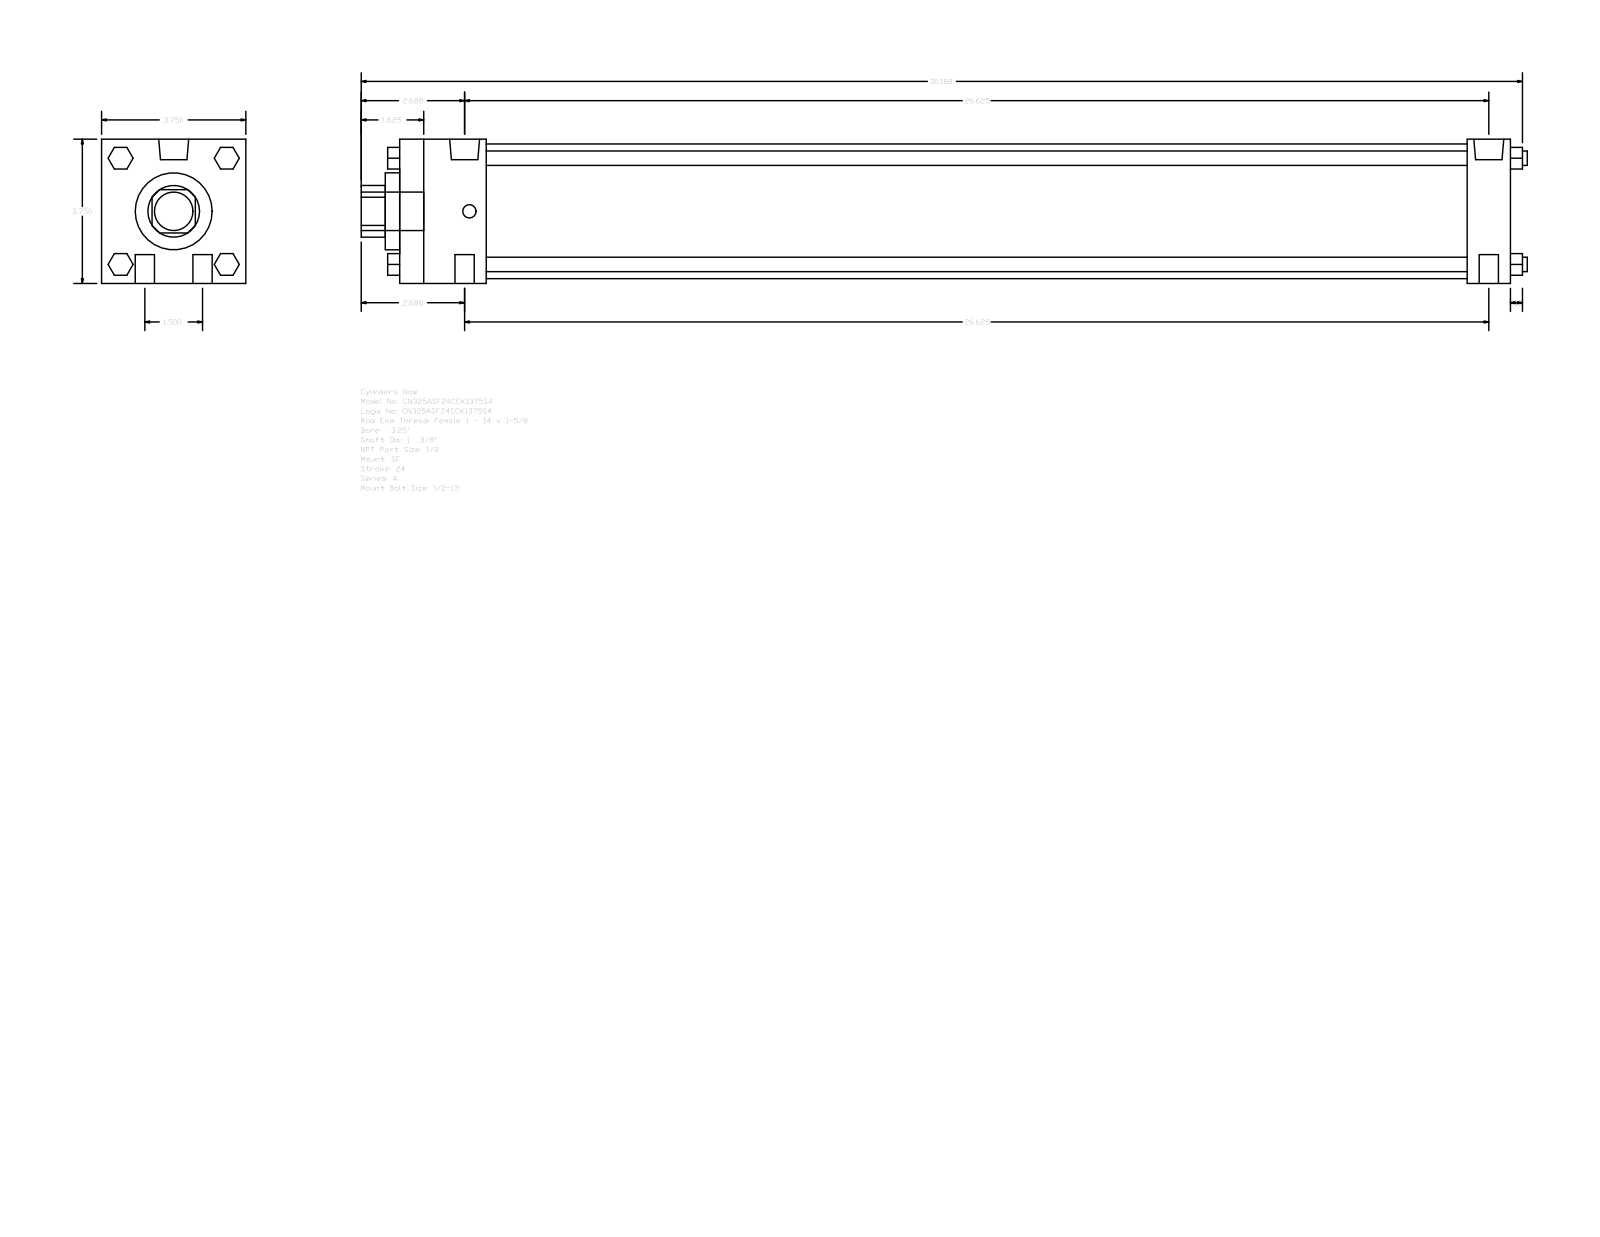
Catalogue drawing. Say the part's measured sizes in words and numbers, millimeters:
The part is named "A_SF__0325_1.375". Its 3-D file was written by "GSSL Pune (CONFIG_CONTROL_DESIGN)". It is 0 solids with 124 faces: 94 planar, 30 cylindrical and 0 other. Overall it measures 769.94 by 95.25 by 95.25 millimeters. Round holes: 1 of diameter 34.92, 1 of diameter 50.8, 1 of diameter 88.9. Round bosses or shafts: 4 of diameter 12.7, 4 of diameter 9.53, 2 of diameter 19.77, 2 of diameter 8.73, 1 of diameter 25.4. Partial cylindrical surfaces (rounded edges, fillets, slot ends): 1 of radius 17.06. The main face-to-face distances are 95.24, 733.43, 28.58, 704.85, 57.15, 647.7, 676.28, 9.52, 66.67, 714.37.
